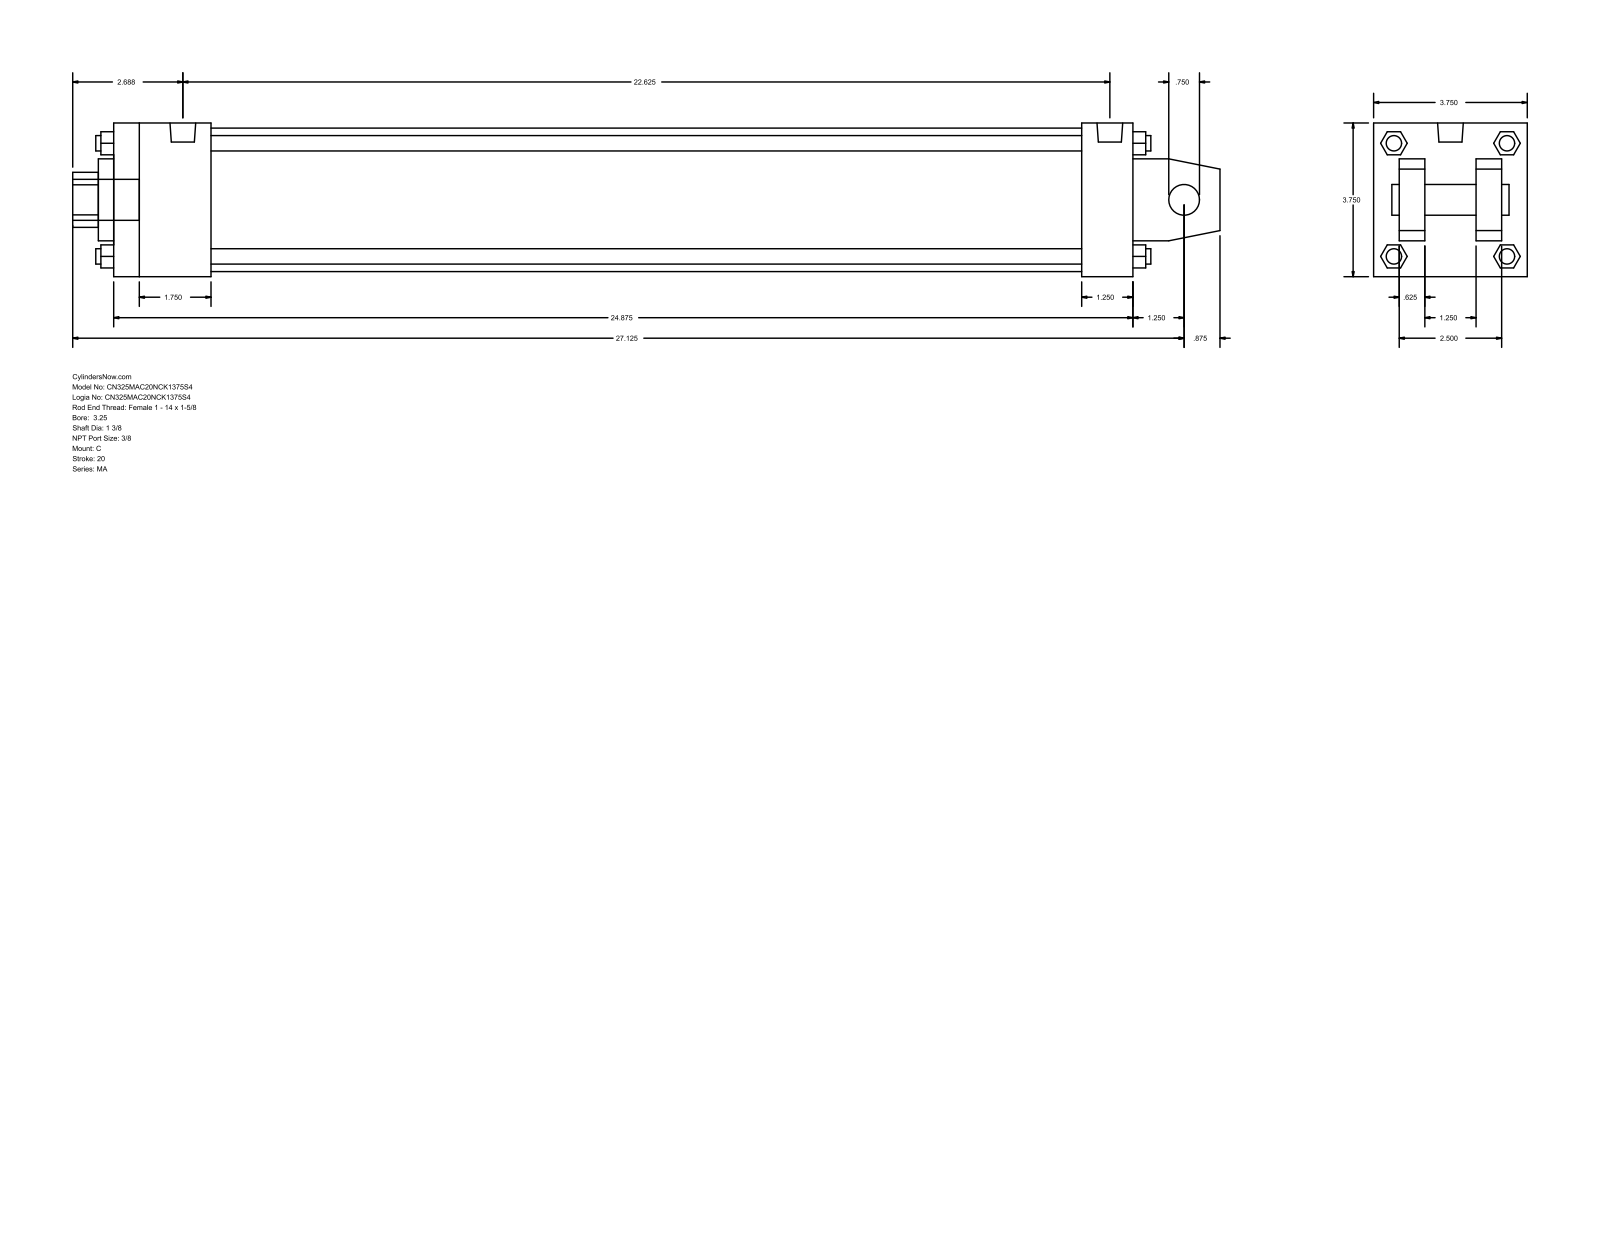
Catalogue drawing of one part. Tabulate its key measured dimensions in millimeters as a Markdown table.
| quantity | value |
| --- | --- |
| part name | MA_C__0325_1.375 |
| STEP written by | GSSL Pune (CONFIG_CONTROL_DESIGN) |
| units | millimeters |
| bodies | 0 solids, 139 faces (108 planar, 31 cylindrical, 0 other) |
| overall size | 711.2 × 95.25 × 95.25 |
| round holes (diameter × count) | 19.05 × 1, 34.92 × 1, 50.8 × 1, 88.9 × 1 |
| round bosses / shafts (diameter × count) | 11.11 × 4, 9.53 × 4, 15.93 × 2, 25.4 × 1 |
| partial cylindrical surfaces (radius × count) | 17.06 × 1 |
| main face-to-face distances | 95.24, 15.87, 63.5, 631.83, 31.74, 79.37, 47.63, 600.08, 31.75, 60.32 |
